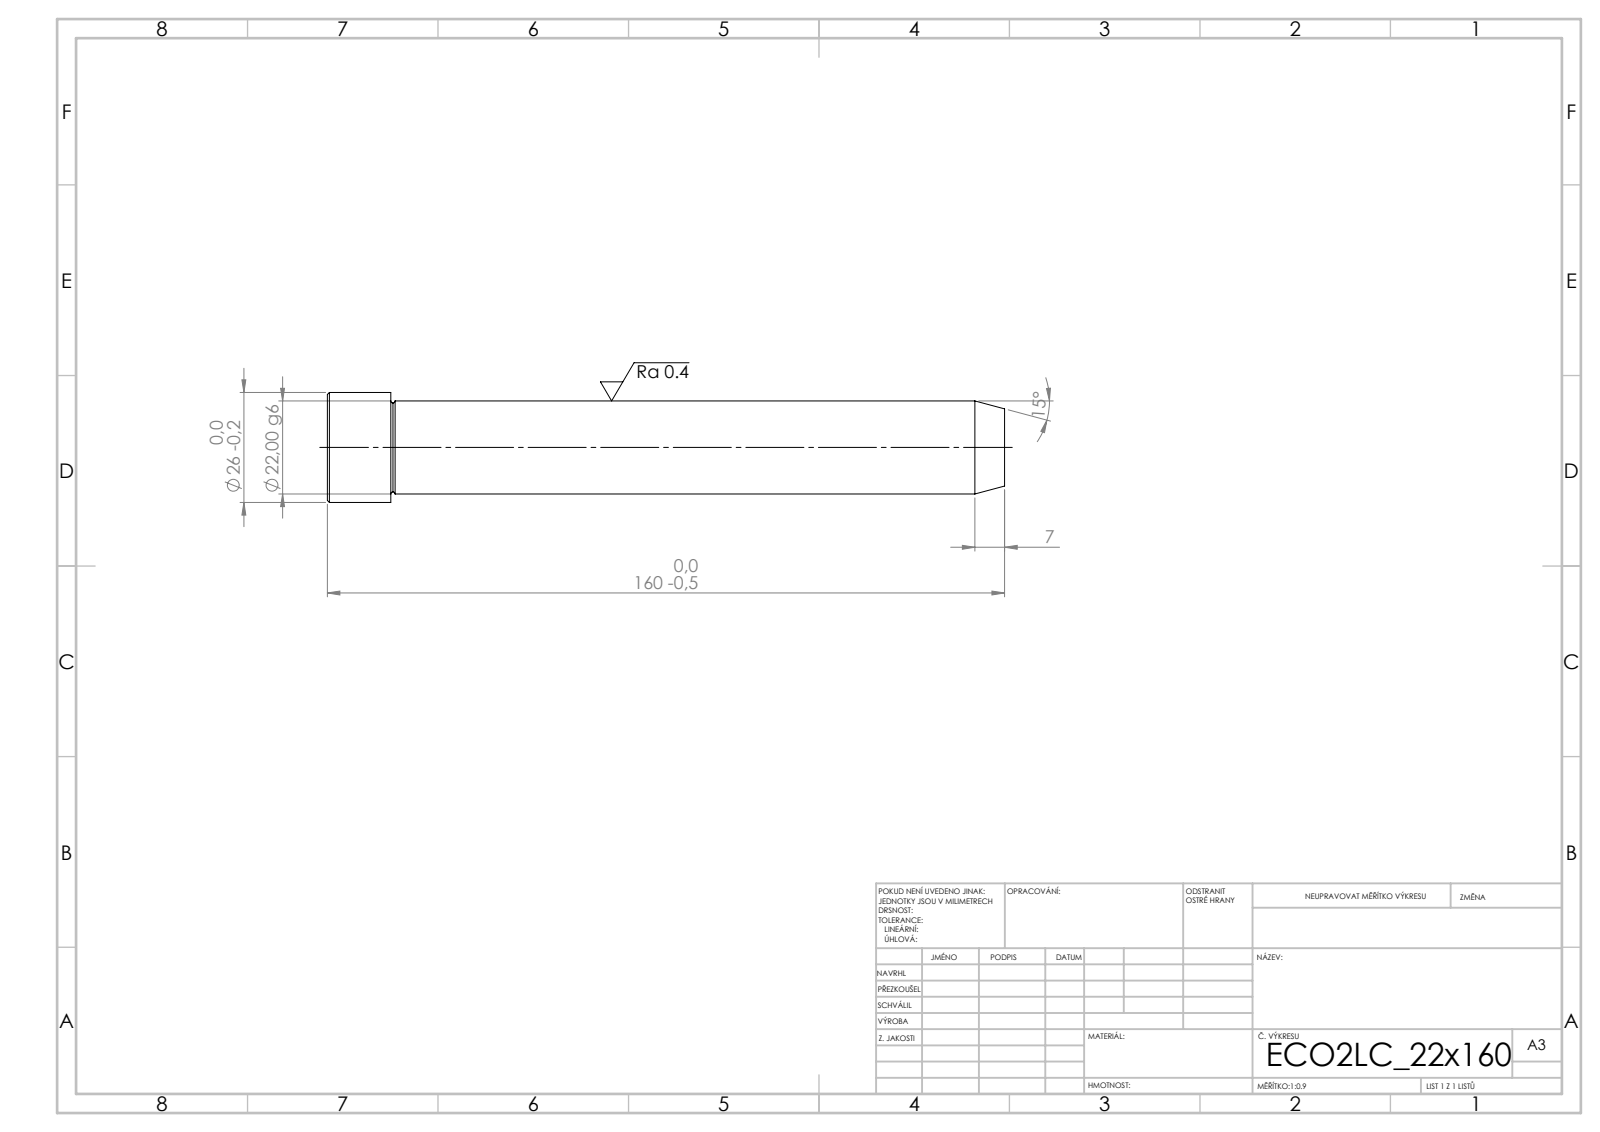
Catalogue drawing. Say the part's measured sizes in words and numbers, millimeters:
Its 3-D file was written by "SolidWorks 2019 (CONFIG_CONTROL_DESIGN)". It is 1 solid with 15 faces: 3 planar, 4 cylindrical and 8 other. Overall it measures 160 by 26 by 26 millimeters. Its volume is 62 619 cubic millimeters and its surface area 12 177 square millimeters. Round bosses or shafts: 1 of diameter 26, 1 of diameter 22. The main face-to-face distances are 160, 145, 15.
